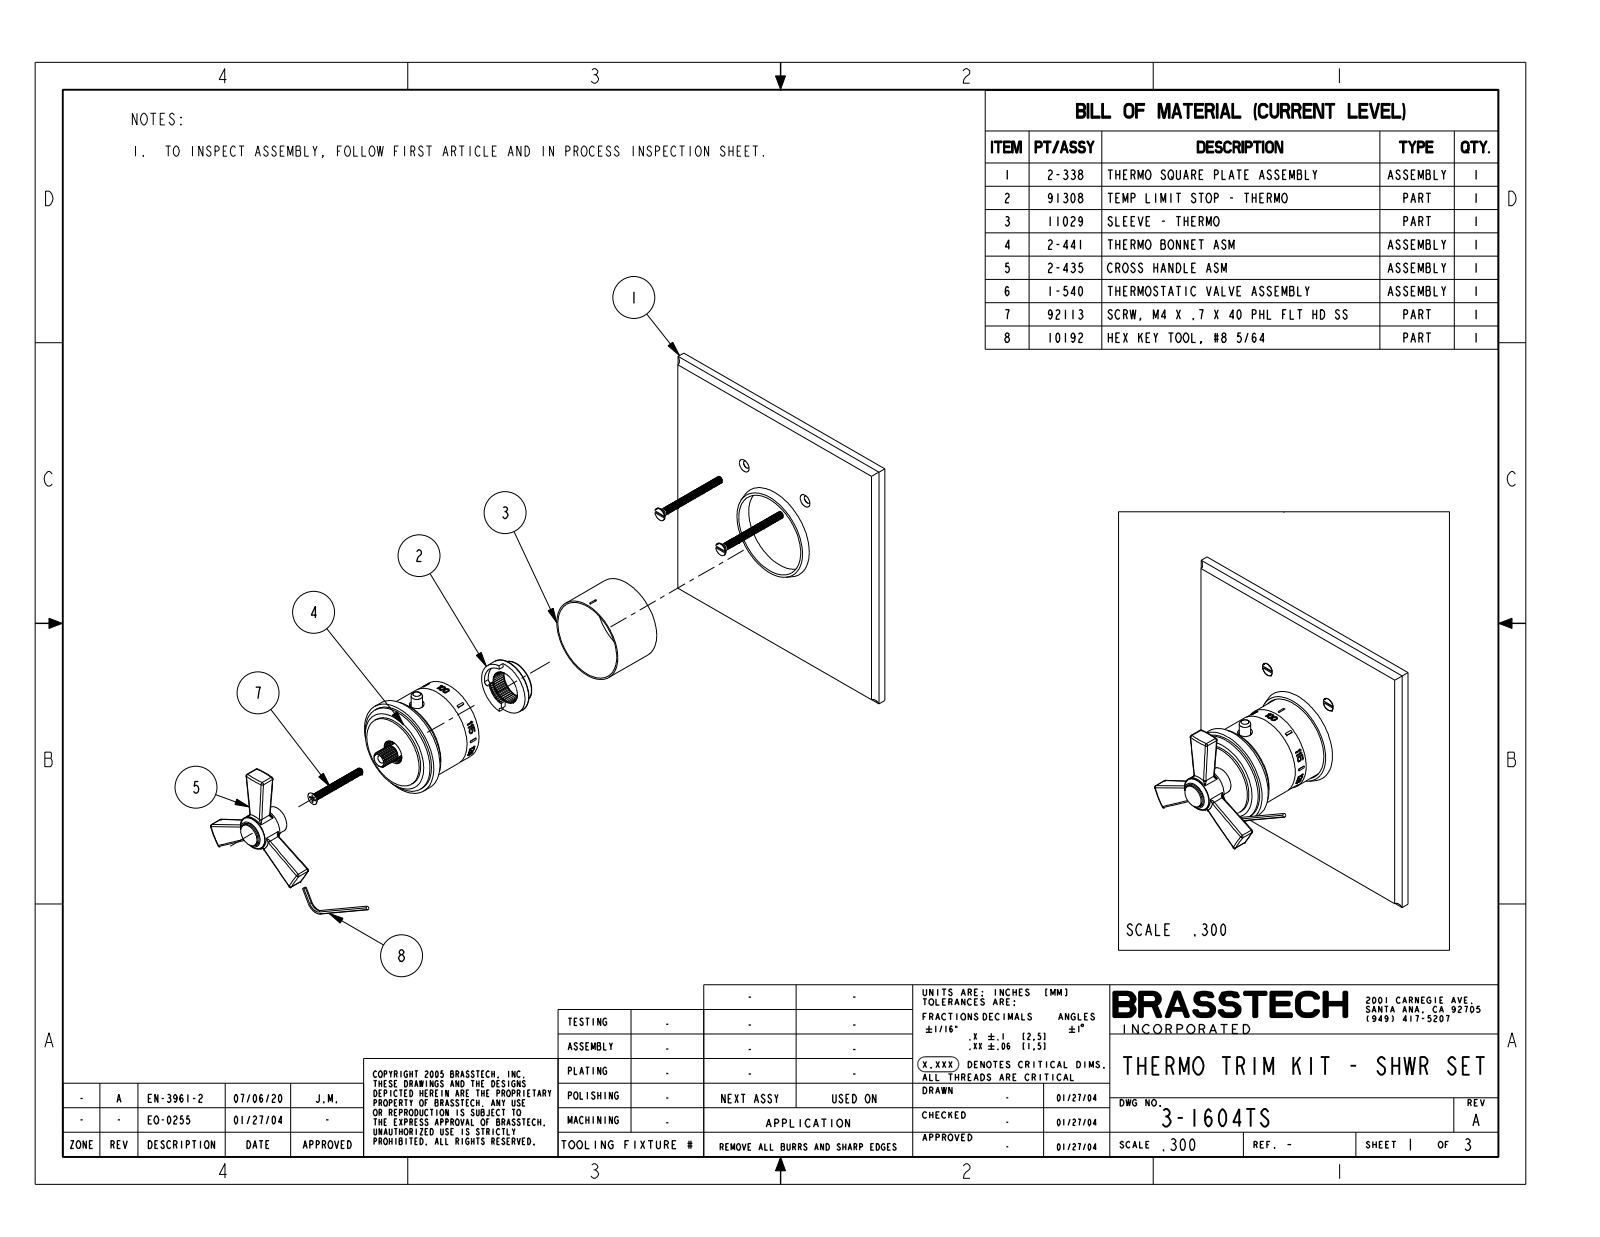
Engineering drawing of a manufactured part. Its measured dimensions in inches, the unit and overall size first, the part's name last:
Units: inches
Overall size (bounding box): 6.5 × 6.5 × 3.705
Round bosses / shafts (diameter × count): ⌀2.24 ×1, ⌀2.09 ×1, ⌀1.97 ×1, ⌀1.94 ×1, ⌀1.929 ×1, ⌀1.69 ×1, ⌀0.8 ×1, ⌀0.625 ×1
Partial cylindrical surfaces — rounded edges, fillets, slot ends (radius × count): R0.04 ×6, R0.1 ×6, R0.125 ×4, R0.969 ×1
Main face-to-face distances: 0.313, 6.5, 2.792, 2.479, 0.2, 0.05, 2.742, 2.429, 0.15, 2.392
Volume: 21.62 in³ · Surface area: 115.8 in²
Bodies: 1 solid, 496 faces (347 planar, 59 cylindrical, 90 other)
Part name (STEP PRODUCT): 3-1604TS
STEP written by: CREO PARAMETRIC BY PTC INC, 2018400 (CONFIG_CONTROL_DESIGN)
